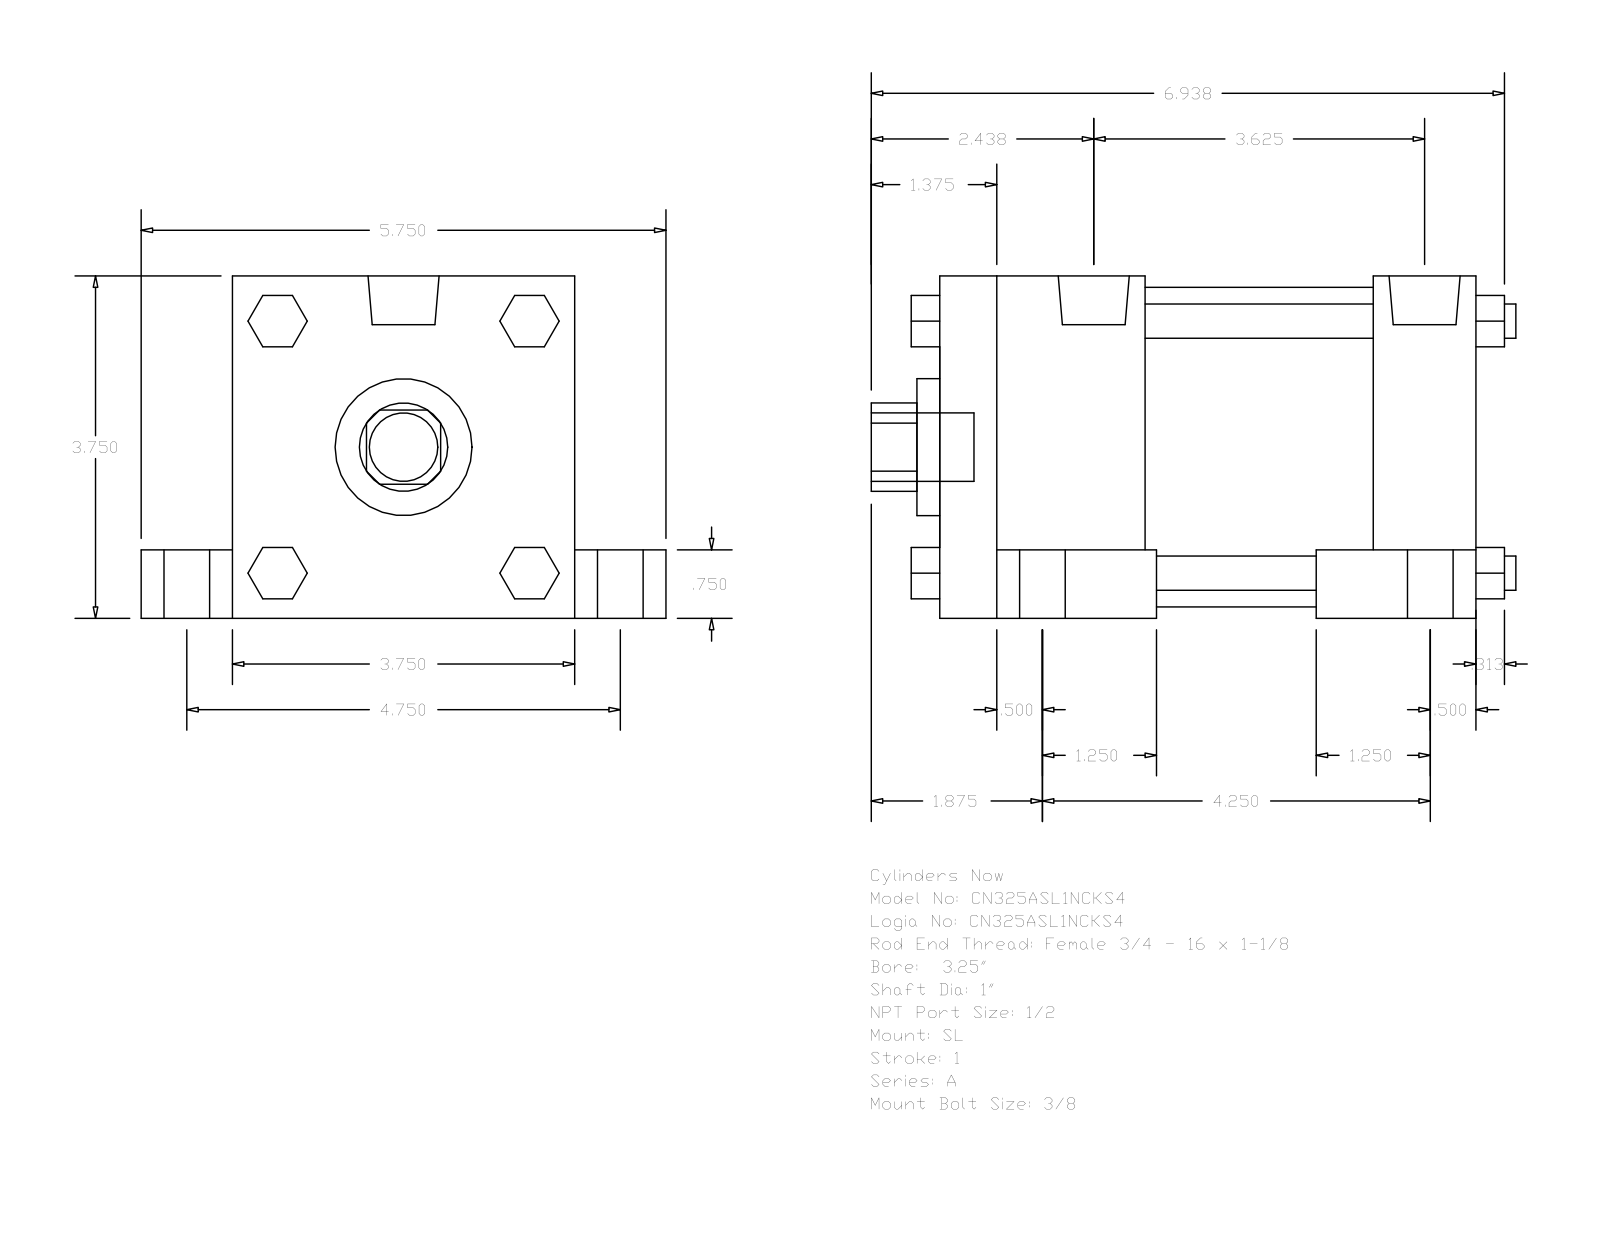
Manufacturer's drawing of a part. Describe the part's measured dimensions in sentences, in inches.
The part is named "A_SL__0325_1". Its 3-D file was written by "GSSL Pune (CONFIG_CONTROL_DESIGN)". It is 0 solids with 150 faces: 114 planar, 36 cylindrical and 0 other. Overall it measures 7.063 by 5.75 by 3.75 inches. Round holes: 1 of diameter 1, 1 of diameter 1.5, 1 of diameter 3.5. Round bosses or shafts: 5 of diameter 0.75, 4 of diameter 0.5, 4 of diameter 0.375, 4 of diameter 0.344, 2 of diameter 0.778. Partial cylindrical surfaces (rounded edges, fillets, slot ends): 1 of radius 0.484. The main face-to-face distances are 3.75, 5.875, 4.75, 0.75, 1, 3, 2.5, 0.625, 2.25, 3.625.
